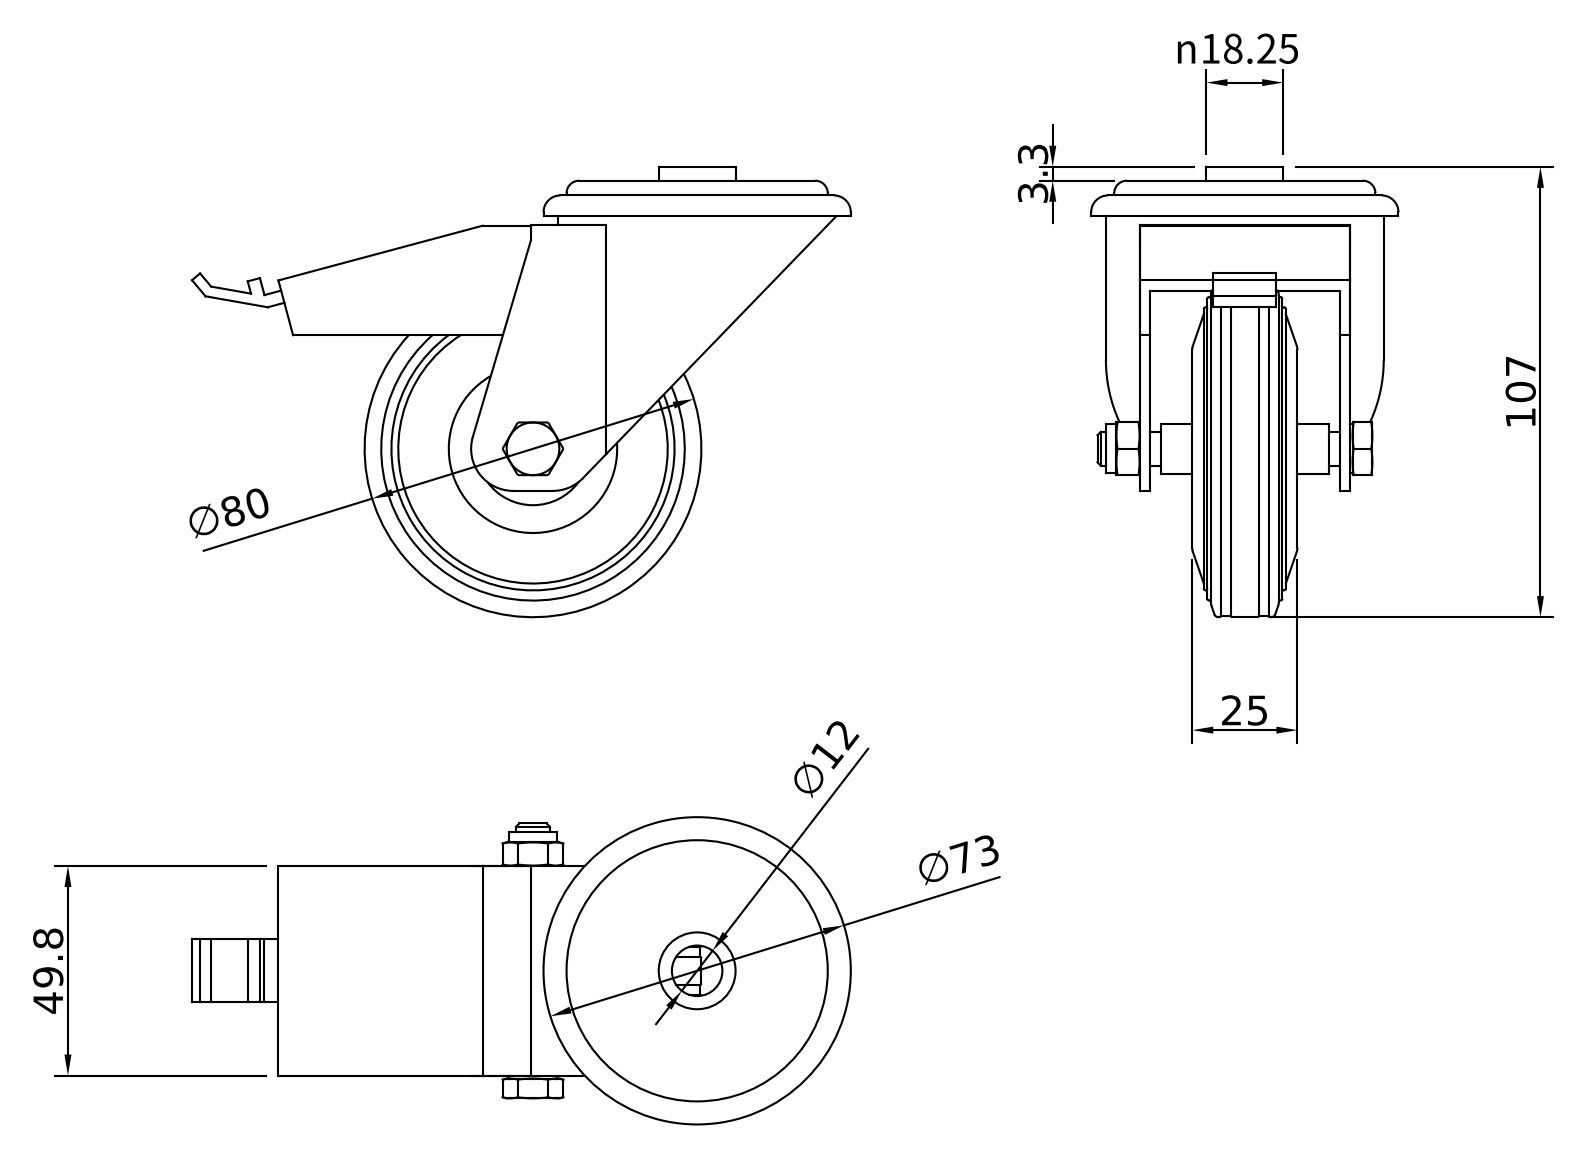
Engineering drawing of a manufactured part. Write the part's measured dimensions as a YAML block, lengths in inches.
part_name: "CRUST0000193; 440000025820; 440000025819; 440000025818"
step_written_by: "Autodesk Inventor 2022 (AUTOMOTIVE_DESIGN)"
units: inches
bodies: {solids: 3, faces: 151, planar: 73, cylindrical: 25, other: 53}
overall_size: [6.161, 4.213, 2.874]
volume: 10.53
surface_area: 88.03
round_holes:
  - {diameter: 0.472, count: 2}
  - {diameter: 2.402, count: 1}
round_bosses_or_shafts:
  - {diameter: 3.15, count: 1}
  - {diameter: 3.126, count: 1}
  - {diameter: 2.874, count: 1}
  - {diameter: 2.598, count: 1}
  - {diameter: 2.443, count: 1}
  - {diameter: 0.719, count: 1}
  - {diameter: 0.458, count: 1}
  - {diameter: 0.315, count: 1}
partial_cylinders:
  - {radius: 0.394, count: 2}
face_to_face_distances: [0.098, 1.87, 1.772, 0.421, 1.965, 0.094, 1.866, 0.492, 1.969, 1.476]
